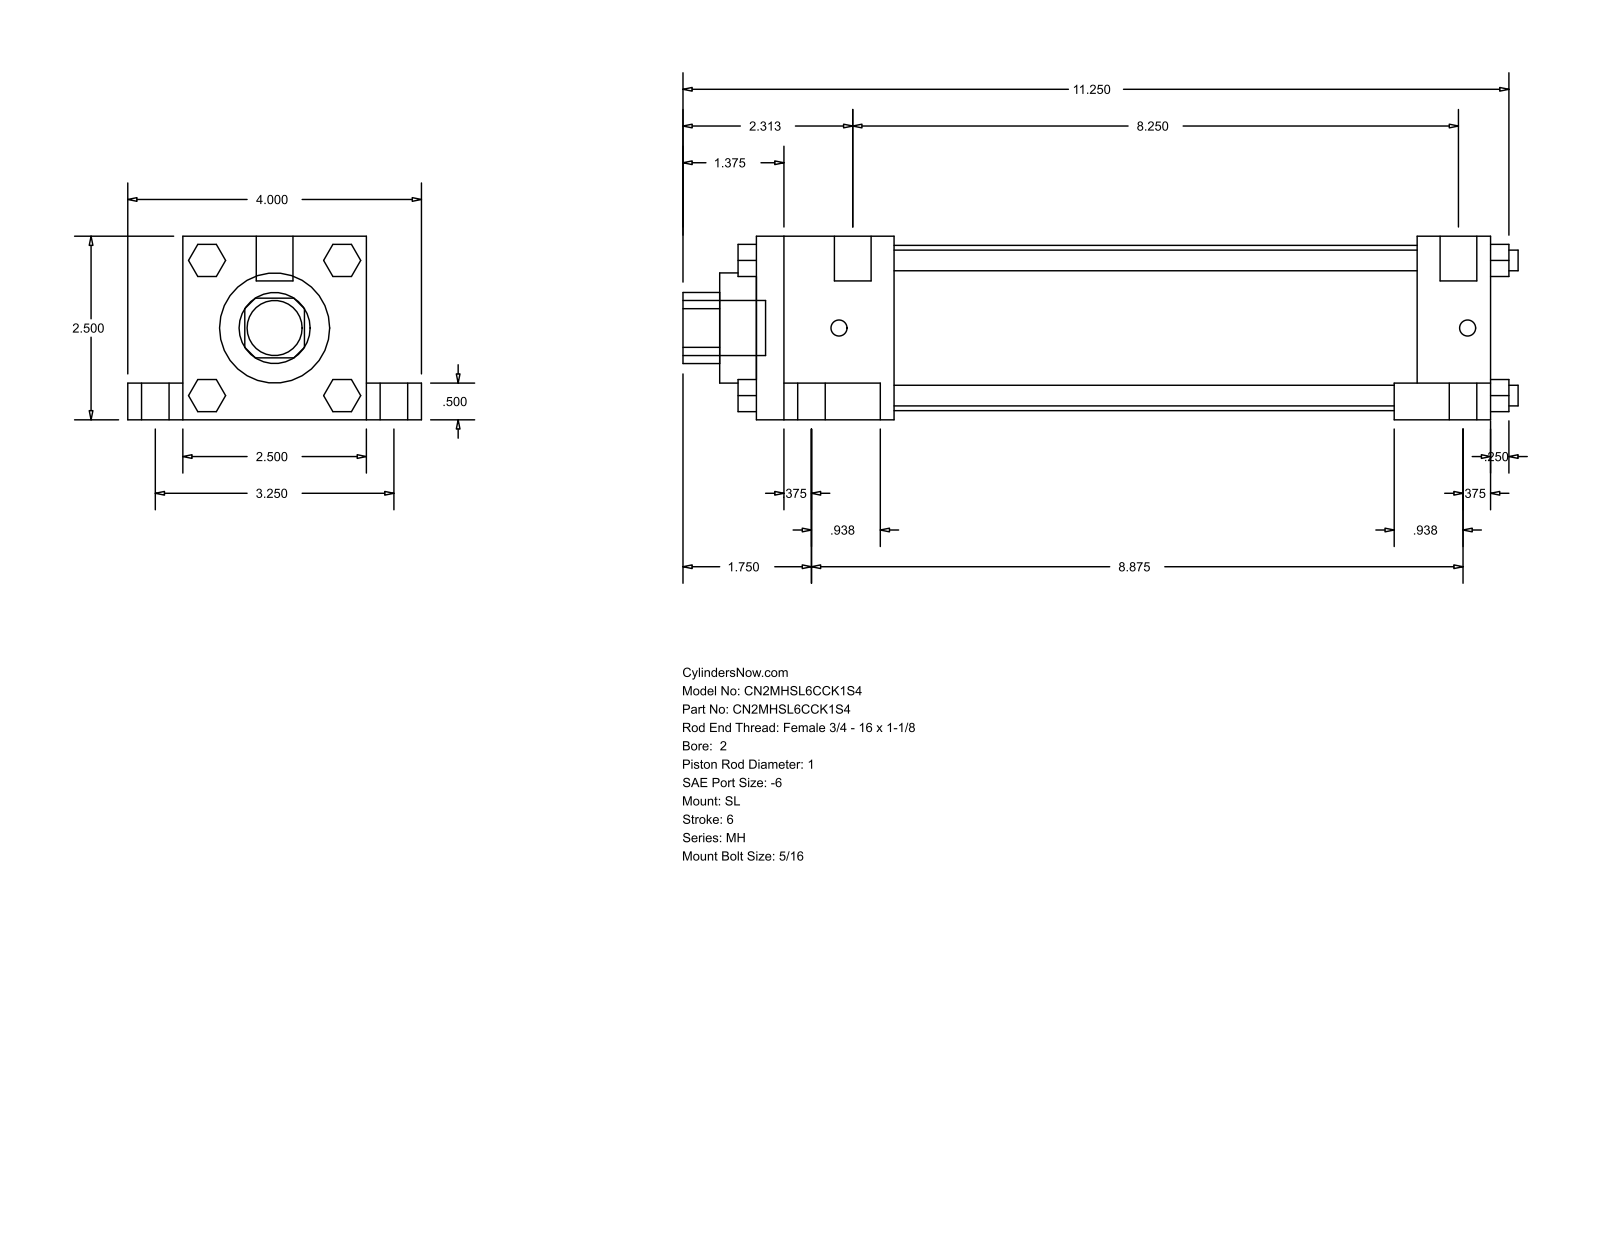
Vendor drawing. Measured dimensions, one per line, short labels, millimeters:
name: MH_SL__0200_1
written by: GSSL Pune (CONFIG_CONTROL_DESIGN)
unit: mm
bodies: 0 solids, 148 faces (112 planar, 36 cylindrical, 0 other)
size: 288.93 × 101.6 × 63.5
holes: 1× ⌀25.4, 1× ⌀38.1, 1× ⌀57.15
bosses: 4× ⌀15.88, 4× ⌀9.53, 4× ⌀7.14, 4× ⌀5.56, 2× ⌀12.7, 1× ⌀19.05
rounds: 1× R12.29
face distances: 63.5, 254, 12.7, 19.05, 50.8, 82.55, 25.4, 9.52, 228.6, 47.63
